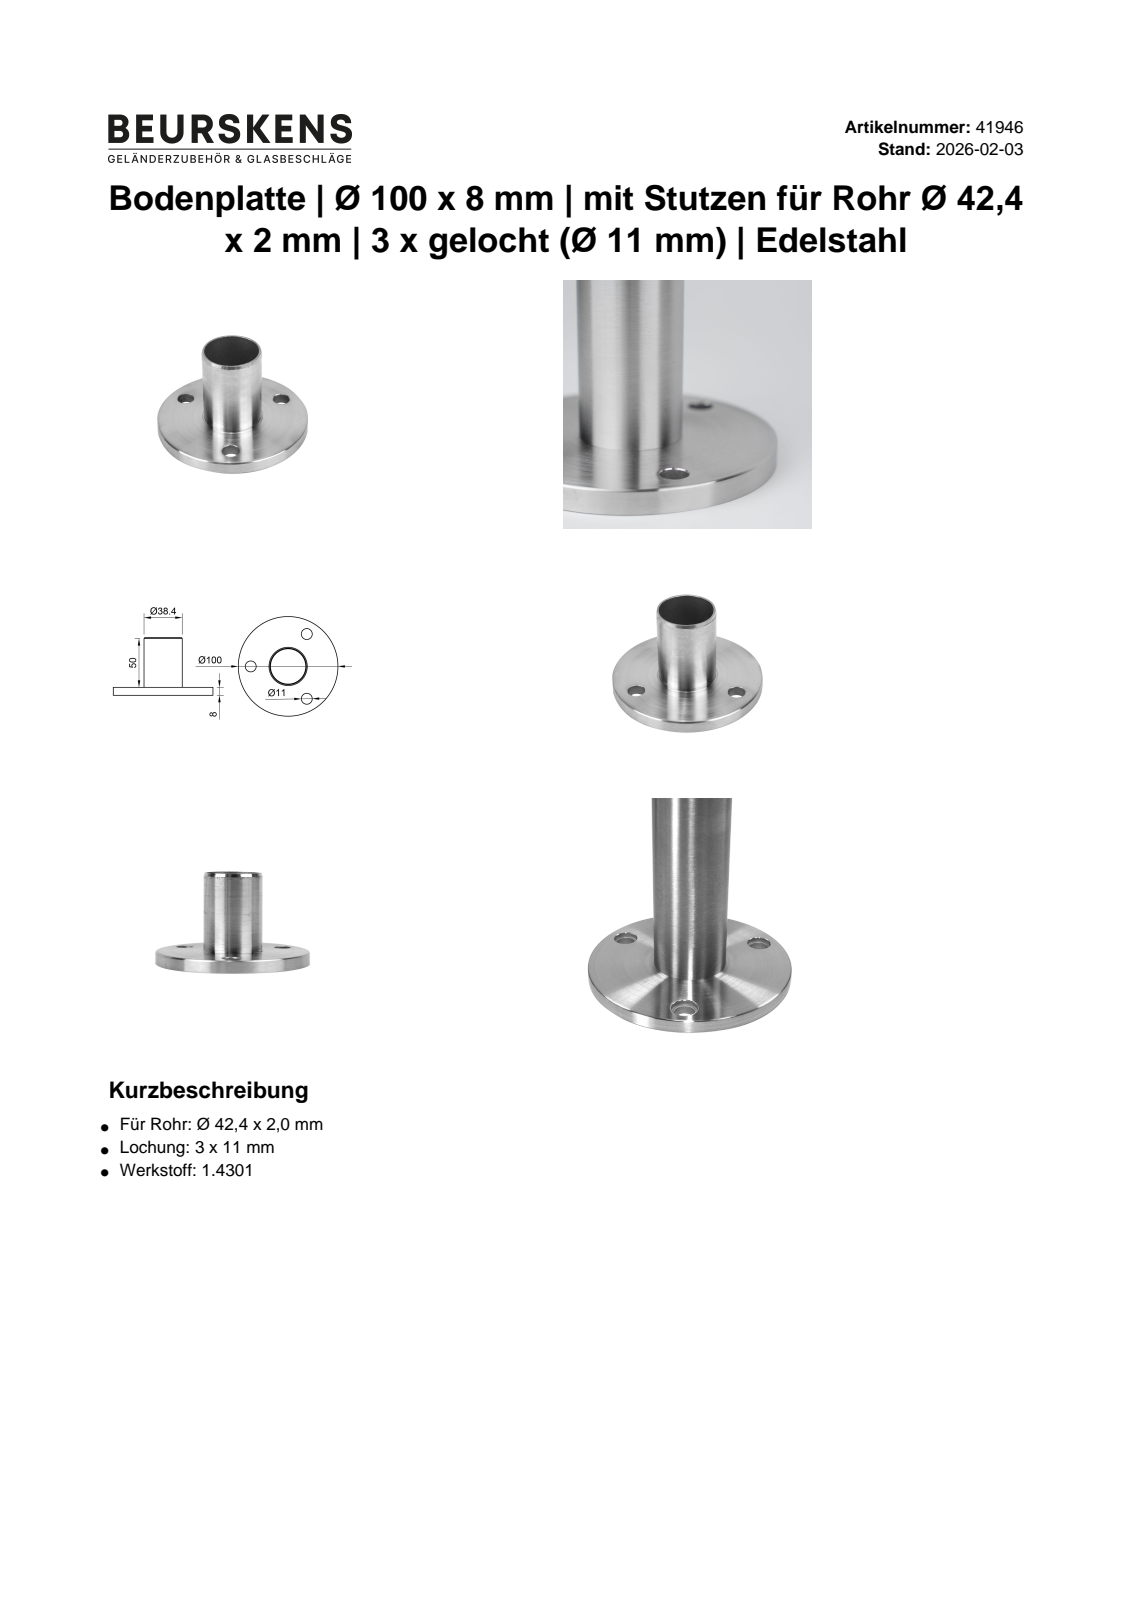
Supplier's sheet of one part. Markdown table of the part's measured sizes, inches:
| quantity | value |
| --- | --- |
| part name | 41946 |
| STEP written by | Autodesk Inventor 2022 (AUTOMOTIVE_DESIGN) |
| units | inches |
| bodies | 1 solid, 11 faces (4 planar, 6 cylindrical, 1 other) |
| overall size | 3.937 × 3.937 × 2.283 |
| volume | 3.997 in³ |
| surface area | 47.15 in² |
| round holes (diameter × count) | 0.433 × 3, 1.394 × 1 |
| round bosses / shafts (diameter × count) | 3.937 × 1, 1.512 × 1 |
| main face-to-face distances | 0.315, 0.167, 0.148, 2.283, 2.116, 1.969 |
| hole center spacings | 1.476, 2.557, 2.557 |
